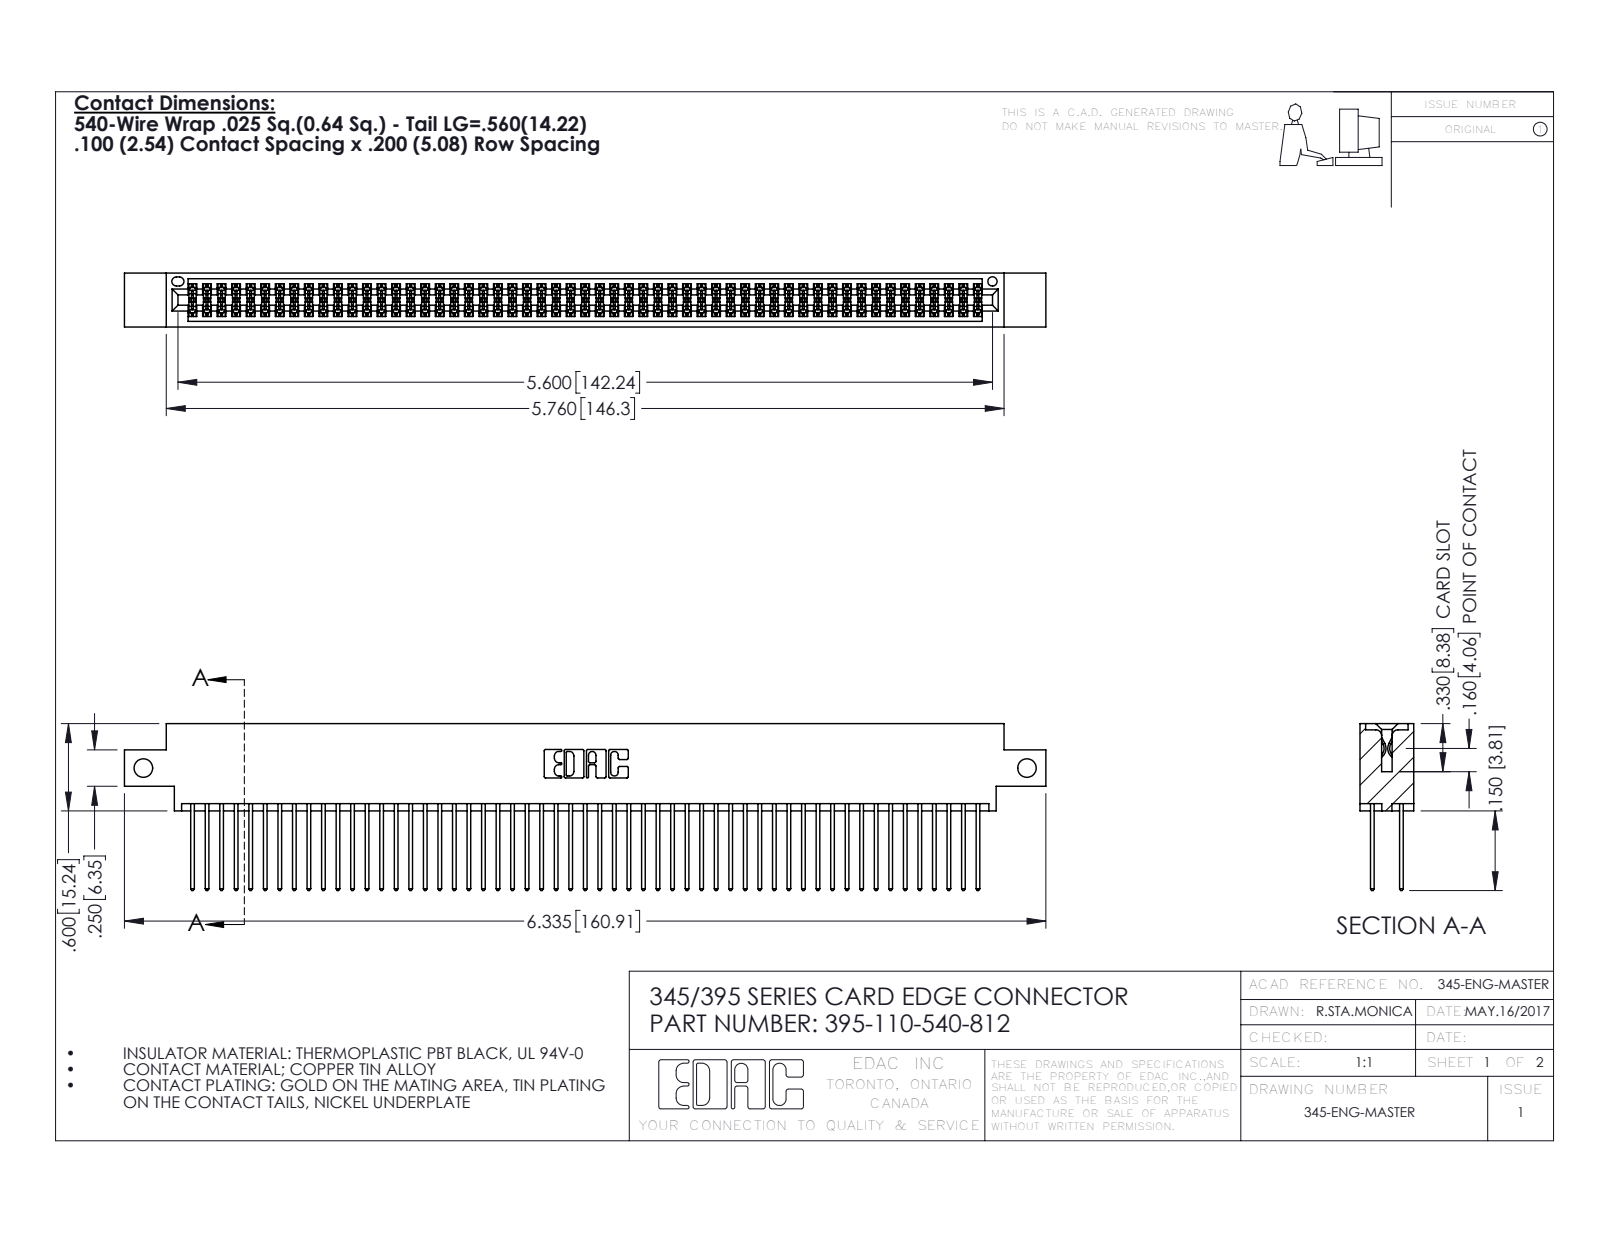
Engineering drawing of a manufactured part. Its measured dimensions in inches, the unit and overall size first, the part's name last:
Units: inches
Overall size (bounding box): 6.335 × 1.147 × 0.37
Round holes (diameter × count): ⌀0.128 ×2, ⌀0.064 ×1
Partial cylindrical surfaces — rounded edges, fillets, slot ends (radius × count): R0.006 ×165, R0.01 ×110, R0.01 ×22, R0.007 ×6, R0.031 ×6, R0.026 ×3, R0.014 ×2, R0.019 ×2
Main face-to-face distances: 0.072, 0.298, 0.2, 0.098, 0.272, 0.025, 0.37, 0.225, 0.175, 0.149
Hole centre spacings: 6.075
Volume: 0.974 in³ · Surface area: 39.99 in²
Bodies: 111 solids, 5630 faces (3714 planar, 1916 cylindrical, 0 other)
Part name (STEP PRODUCT): 345-292-001_345-293-140; 345 Part_0.170 Offset - Side Mount; 395-110-540-812
STEP written by: SolidWorks 2016 (CONFIG_CONTROL_DESIGN)
